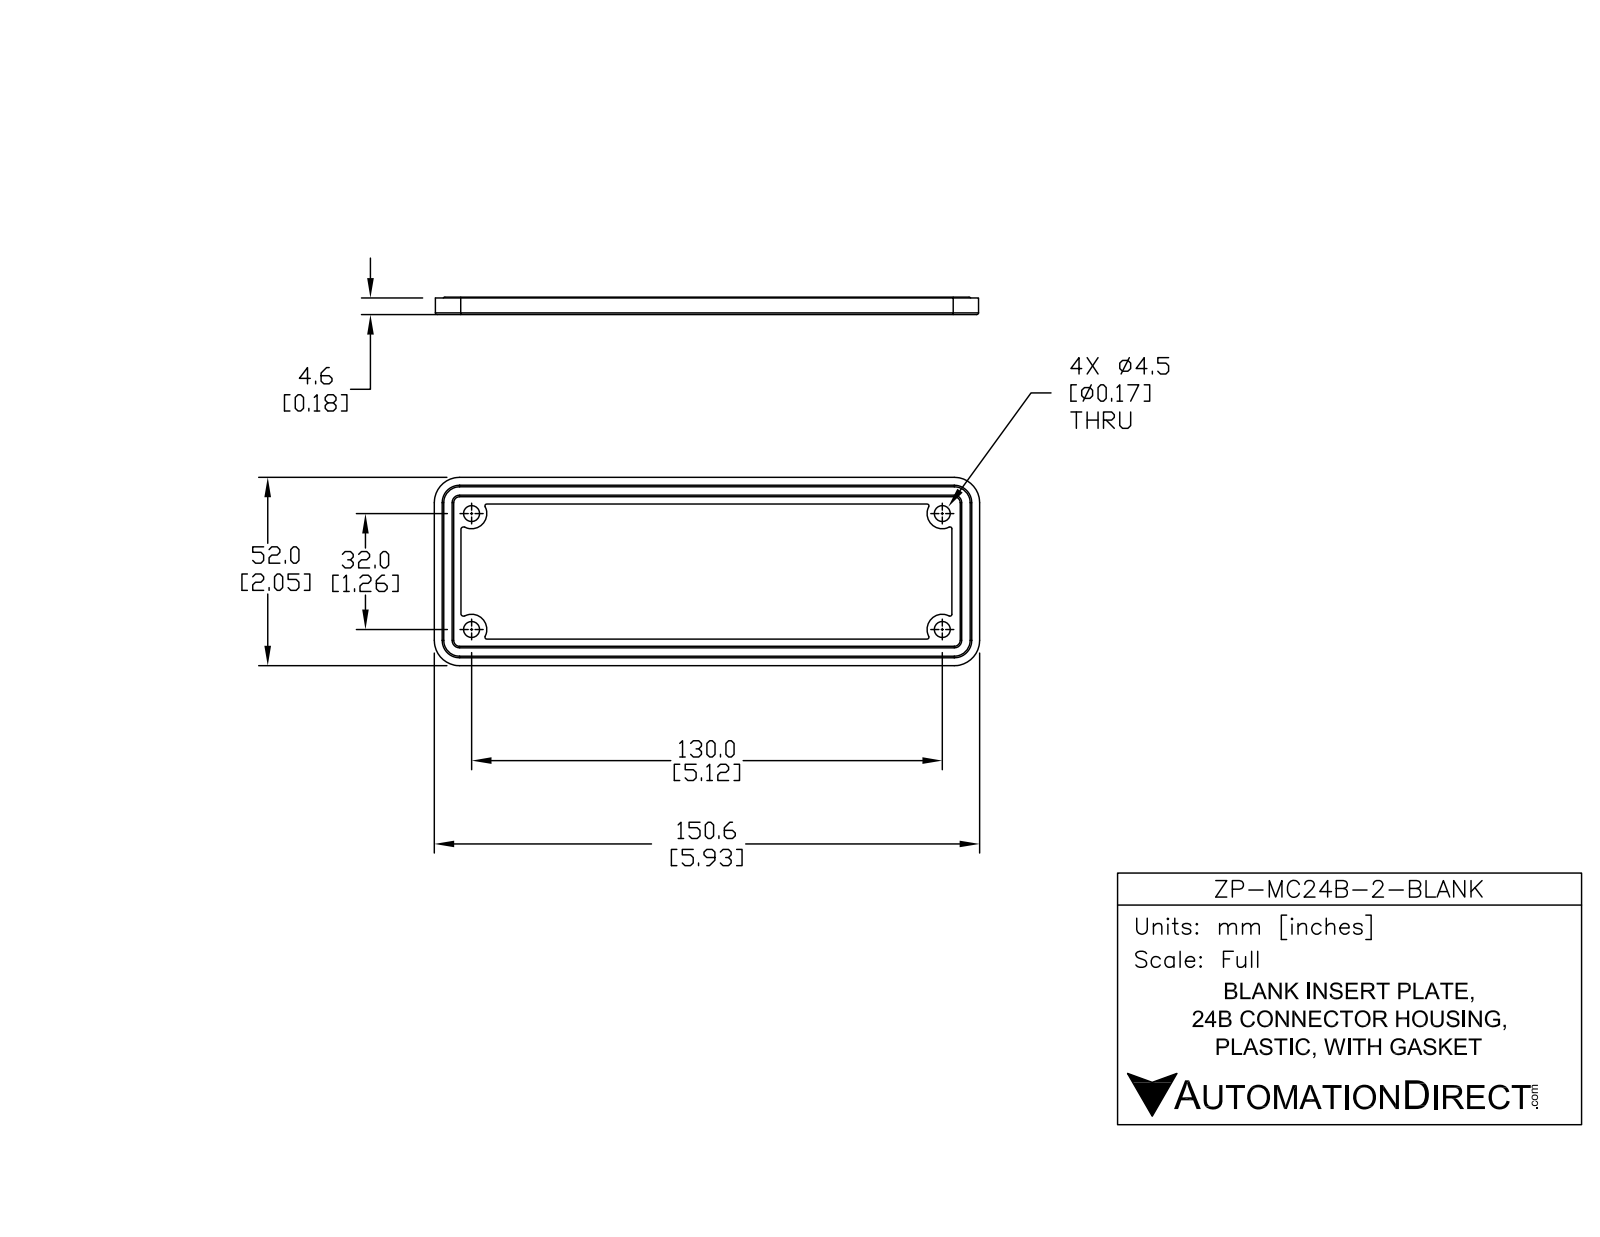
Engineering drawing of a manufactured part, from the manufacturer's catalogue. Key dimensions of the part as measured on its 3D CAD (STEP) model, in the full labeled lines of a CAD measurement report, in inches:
Part name (STEP PRODUCT): ZP-MC24B-2-BLANK
STEP written by: SolidWorks 2014 (AUTOMOTIVE_DESIGN)
Units: inches
Bodies: 1 solid, 65 faces (13 planar, 40 cylindrical, 12 other)
Overall size (bounding box): 5.929 × 2.047 × 0.191
Volume: 1.289 in³ · Surface area: 28.72 in²
Round holes (diameter × count): ⌀0.173 ×4
Partial cylindrical surfaces — rounded edges, fillets, slot ends (radius × count): R0.02 ×20, R0.165 ×4, R0.276 ×4
Main face-to-face distances: 0.063, 0.118, 0.181, 0.29, 0.128, 0.191, 1.757, 2.047, 1.468, 5.929
Hole centre spacings: 1.26, 5.118, 5.271
